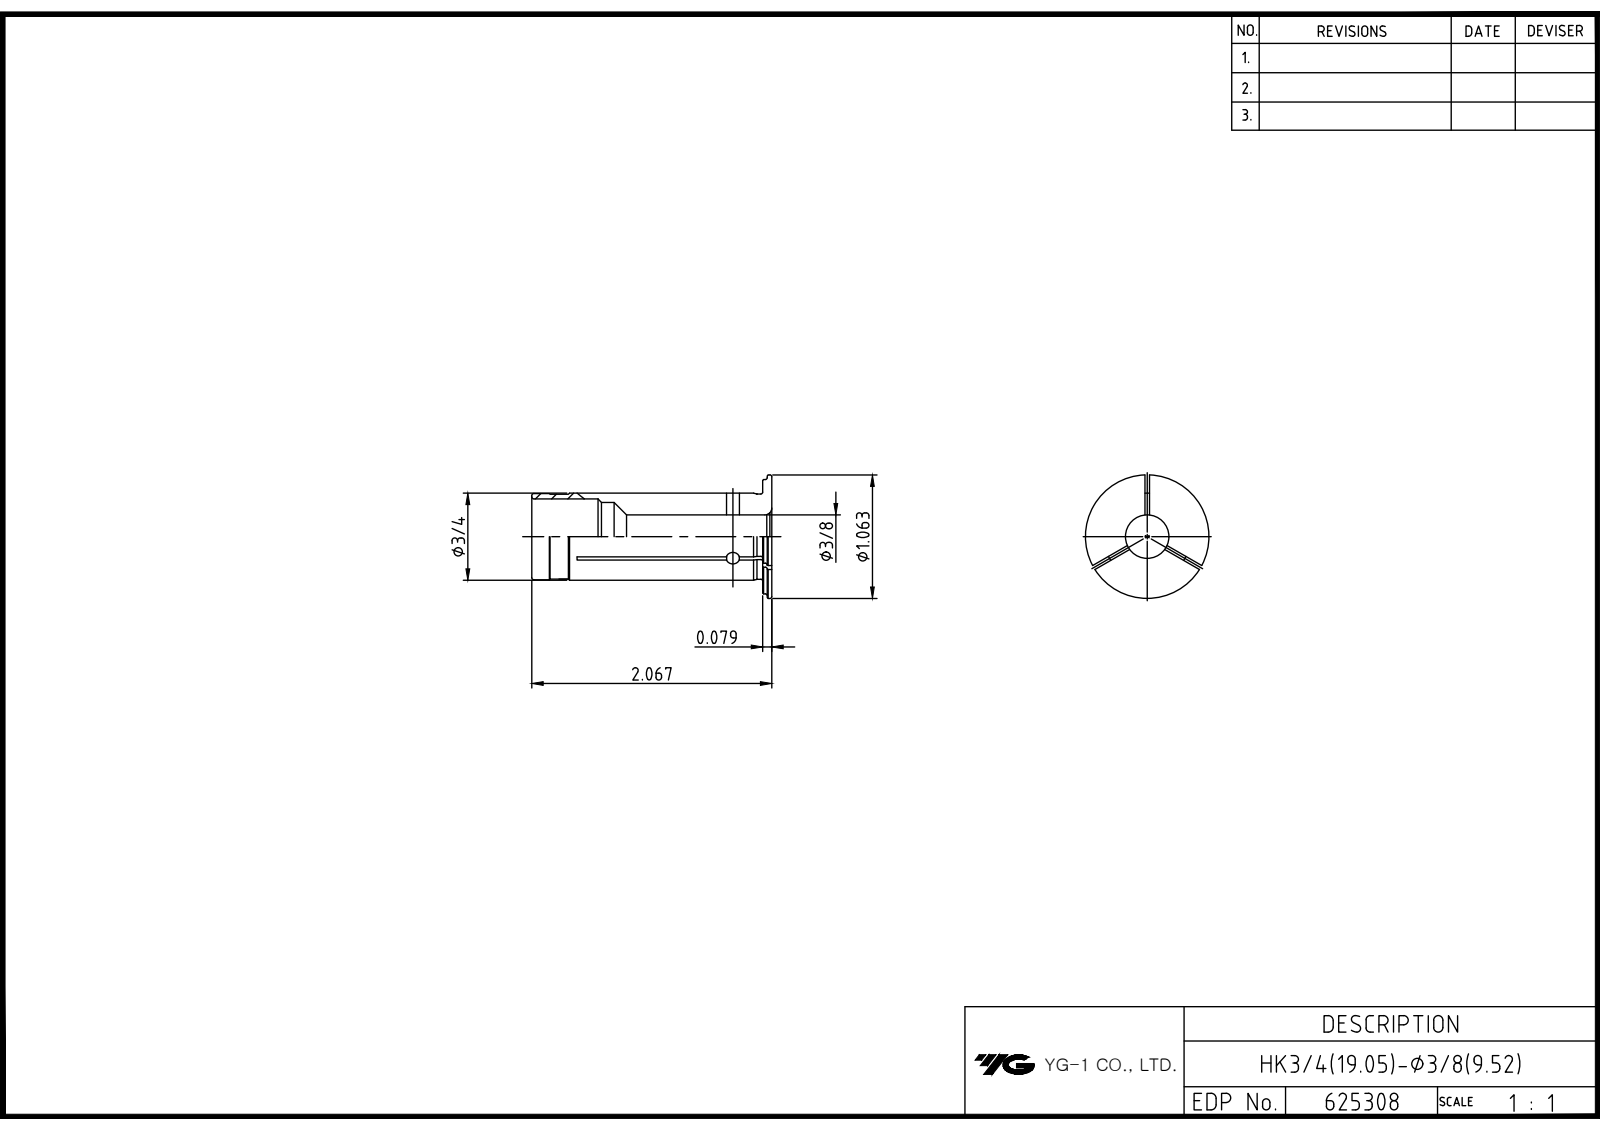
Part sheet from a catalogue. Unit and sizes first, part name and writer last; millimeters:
Units: millimetres
Overall size (bounding box): 52.5 × 27 × 26.99
Round holes (diameter × count): ⌀9.53 ×1, ⌀15 ×1, ⌀16.5 ×1
Round bosses / shafts (diameter × count): ⌀27 ×1, ⌀25 ×1, ⌀19.05 ×1, ⌀18.85 ×1, ⌀18.65 ×1, ⌀18.55 ×1
Partial cylindrical surfaces — rounded edges, fillets, slot ends (radius × count): R1.45 ×3, R37.5 ×3
Main face-to-face distances: 1, 2, 50.5, 51.5, 52.5
Volume: 8 412 mm³ · Surface area: 6 774 mm²
Bodies: 1 solid, 92 faces (22 planar, 32 cylindrical, 38 other)
Part name (STEP PRODUCT): HK19_05-9_525
STEP written by: PRO/ENGINEER BY PARAMETRIC TECHNOLOGY CORPORATION, 2012130 (CONFIG_CONTROL_DESIGN)
